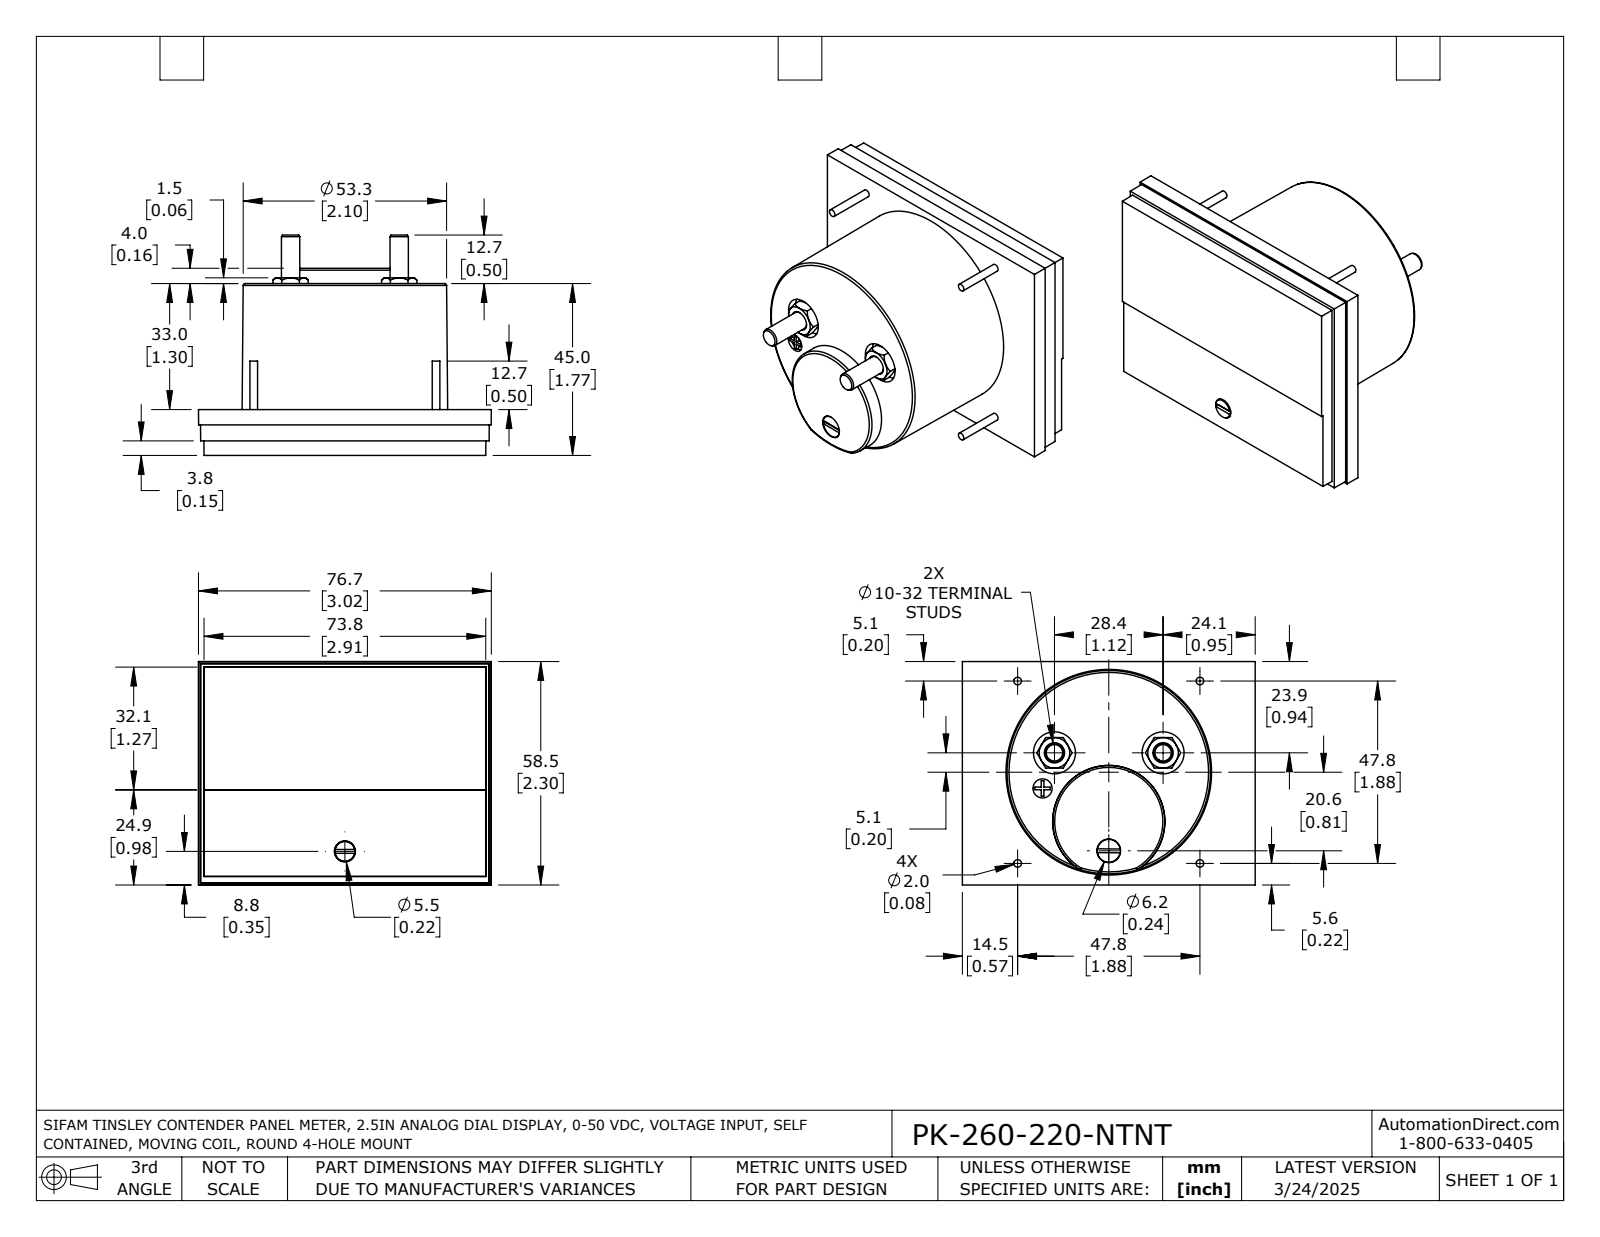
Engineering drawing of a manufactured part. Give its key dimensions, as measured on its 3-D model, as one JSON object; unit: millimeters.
{"part_name": "PK-260-220-NTNT", "step_written_by": "SolidWorks 2021 (AUTOMOTIVE_DESIGN)", "units": "millimeters", "bodies": {"solids": 1, "faces": 192, "planar": 95, "cylindrical": 37, "other": 60}, "overall_size": [76.7, 58.5, 57.7], "volume_mm3": 125500, "surface_area_mm2": 23580, "round_holes": [[5, 3], [11, 2], [5.3, 1], [5.5, 1], [6.2, 1]], "round_bosses_or_shafts": [[2, 4], [4.8, 2], [6, 1], [5.2, 1]], "partial_cylinders_radius": [[0.8, 1]], "face_to_face_distances": [0.5, 12, 3.3, 8.2, 3.8, 11.5, 1.4, 2, 10.1, 1.9], "hole_center_spacings": [29.3, 29.5, 9.8, 23.8, 23.9, 28.4, 32.9]}
